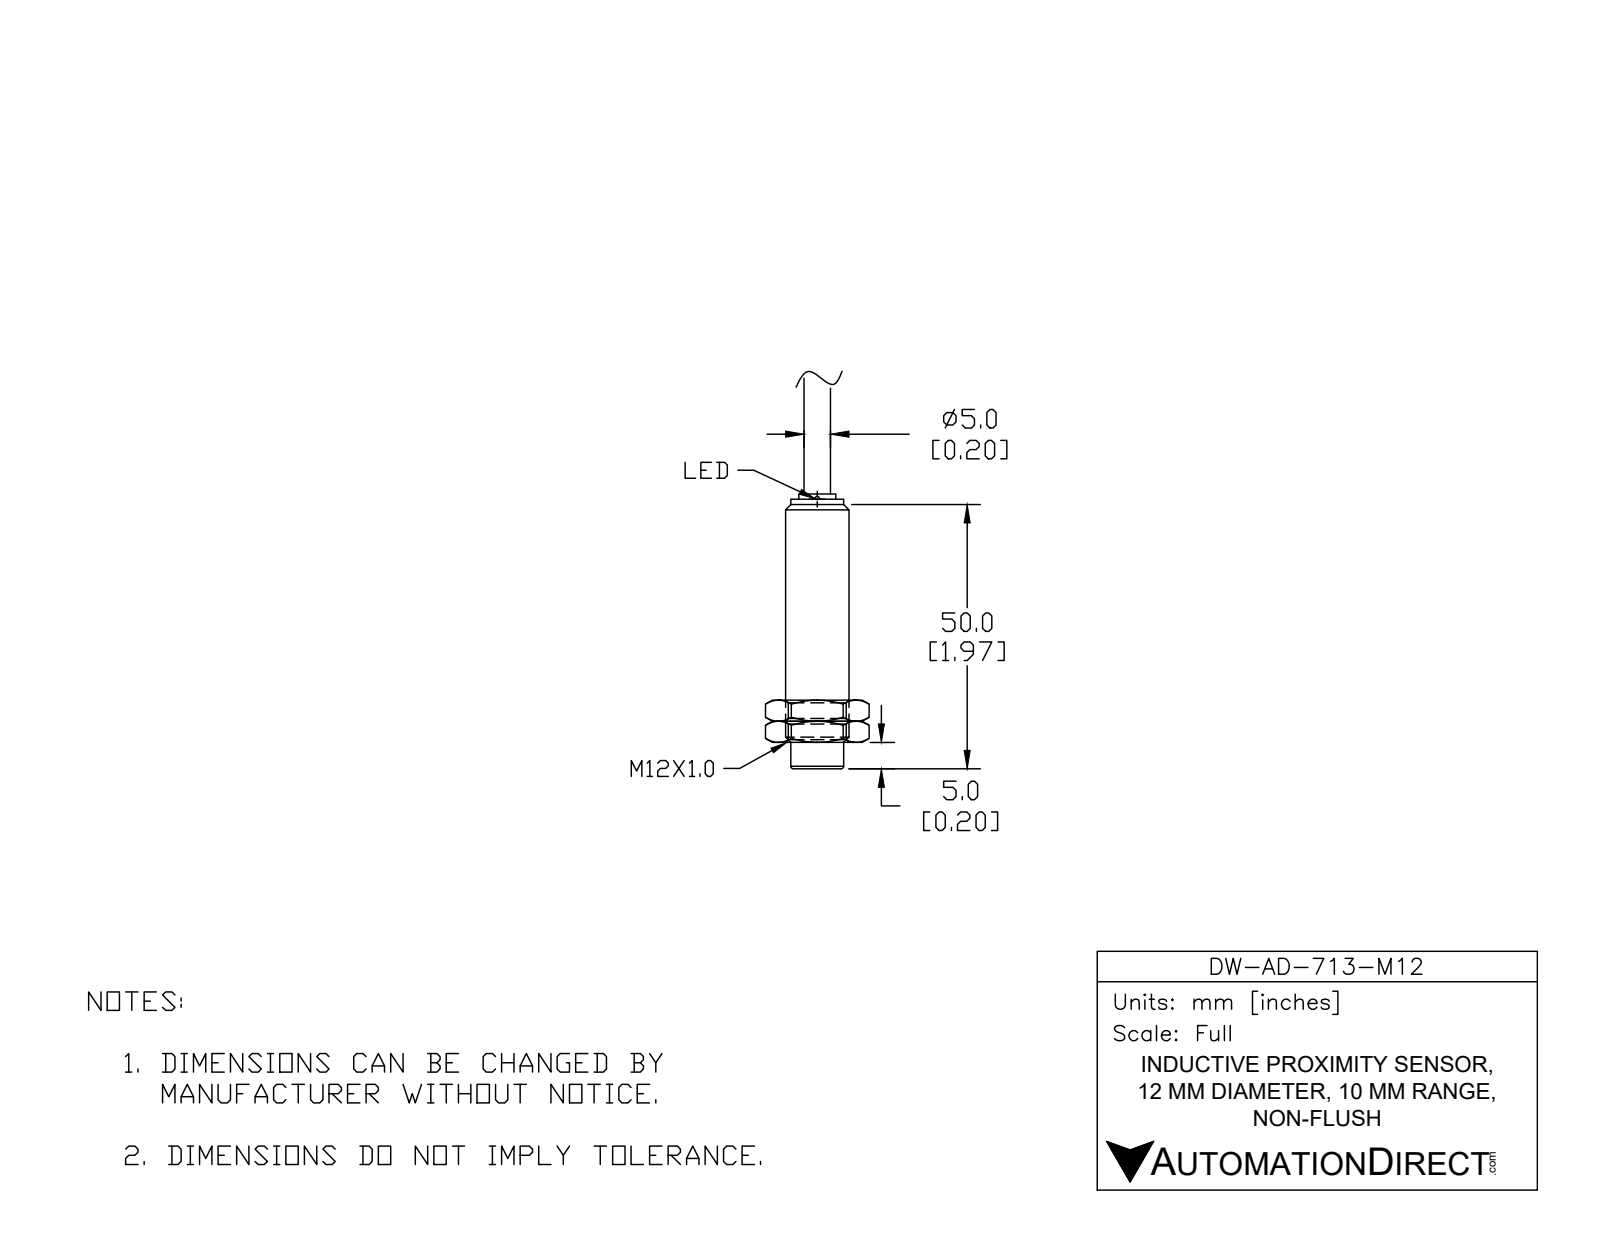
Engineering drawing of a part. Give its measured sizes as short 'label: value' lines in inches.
name: DW-AD-713-M12
written by: SolidWorks 2017 (AUTOMOTIVE_DESIGN)
unit: in
bodies: 2 solids, 34 faces (17 planar, 6 cylindrical, 11 other)
size: 2.976 × 0.472 × 0.472
volume: 0.377 in³; area: 4.017 in²
bosses: 1× ⌀0.472, 1× ⌀0.415, 1× ⌀0.413, 1× ⌀0.268, 1× ⌀0.197, 1× ⌀0.118
face distances: 2.047, 2, 0.047, 1.85, 0.15, 0.197, 2.031, 0.181, 0.031, 0.016
